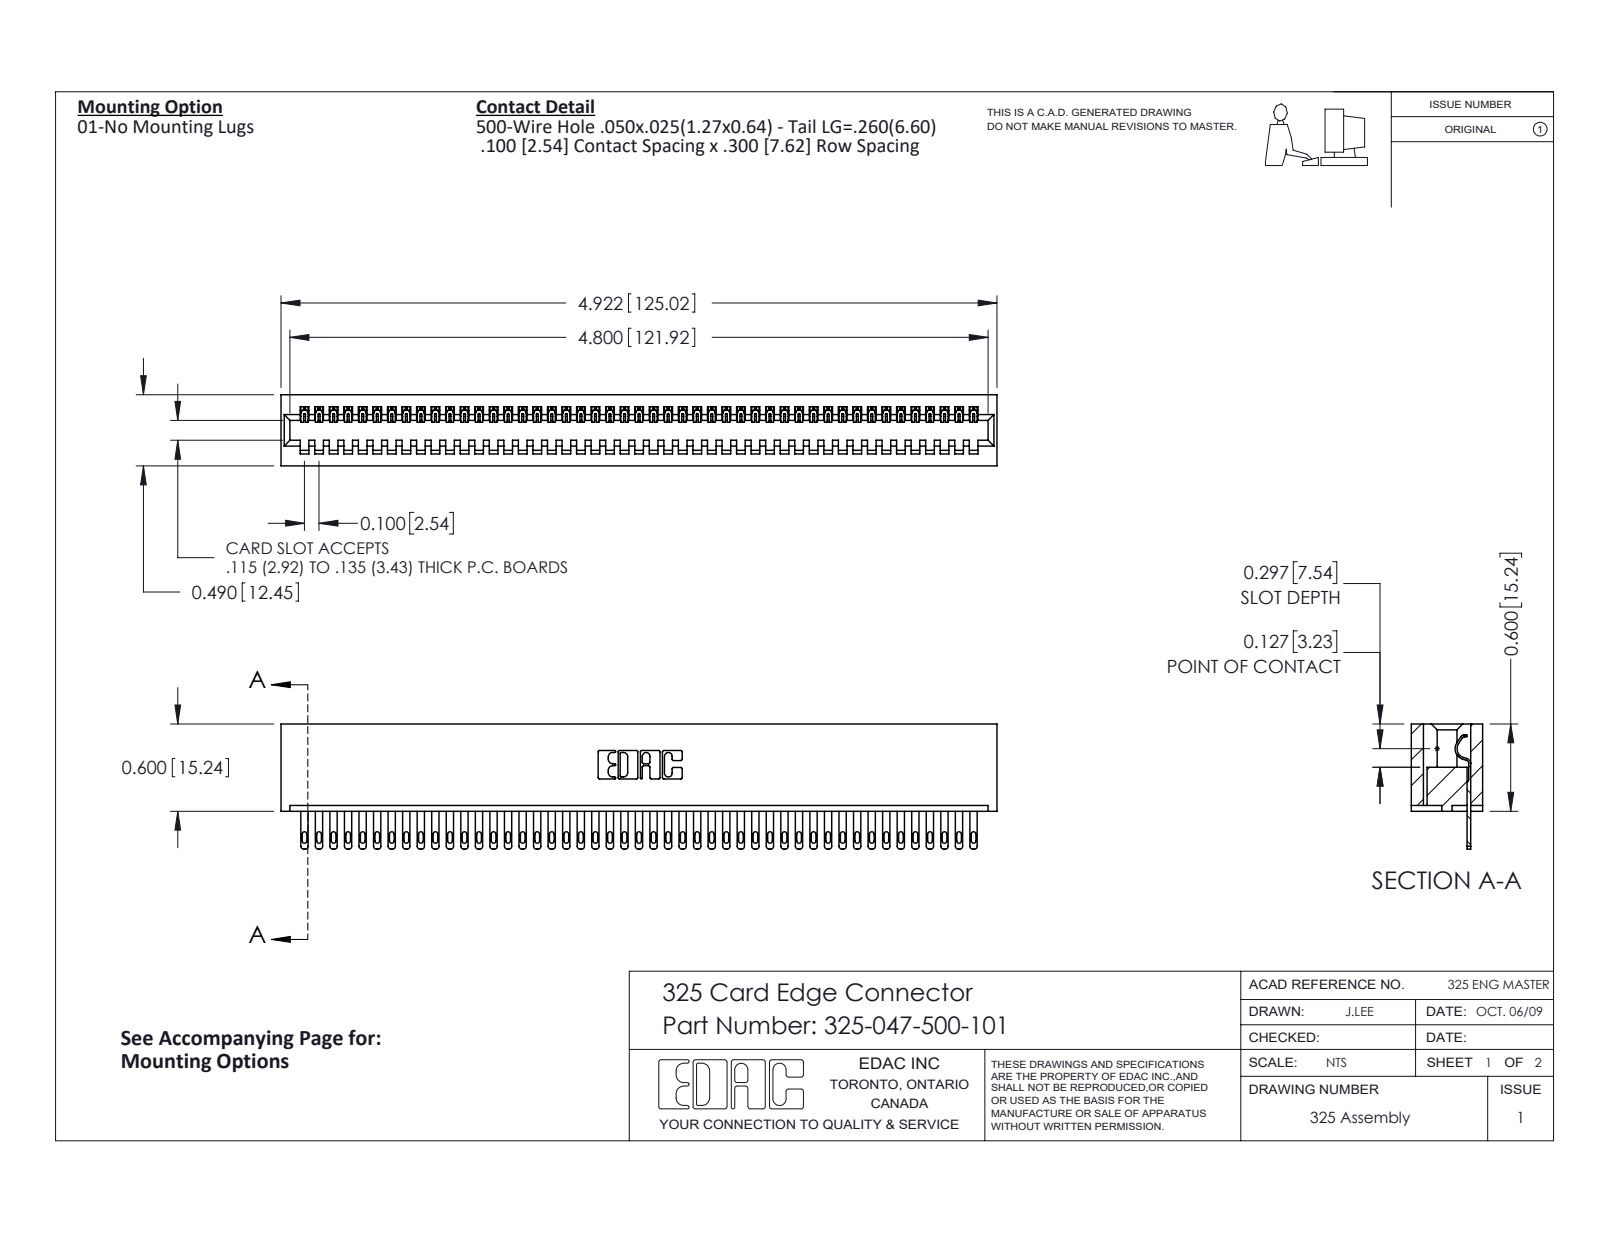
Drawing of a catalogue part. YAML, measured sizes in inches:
part_name: "325 Part_Lugless; 325-292-001_325-293-100; 325-047-500-101"
step_written_by: "SolidWorks 2016 (CONFIG_CONTROL_DESIGN)"
units: inches
bodies: {solids: 48, faces: 2644, planar: 1758, cylindrical: 886, other: 0}
overall_size: [4.922, 0.86, 0.49]
volume: 1.008
surface_area: 29.02
partial_cylinders:
  - {radius: 0.006, count: 94}
  - {radius: 0.016, count: 94}
  - {radius: 0.02, count: 94}
  - {radius: 0.01, count: 22}
  - {radius: 0.007, count: 6}
  - {radius: 0.031, count: 6}
  - {radius: 0.026, count: 3}
  - {radius: 0.014, count: 1}
face_to_face_distances: [0.083, 0.407, 0.49, 0.3, 0.107, 0.383, 0.025, 0.325, 0.56, 0.263]
